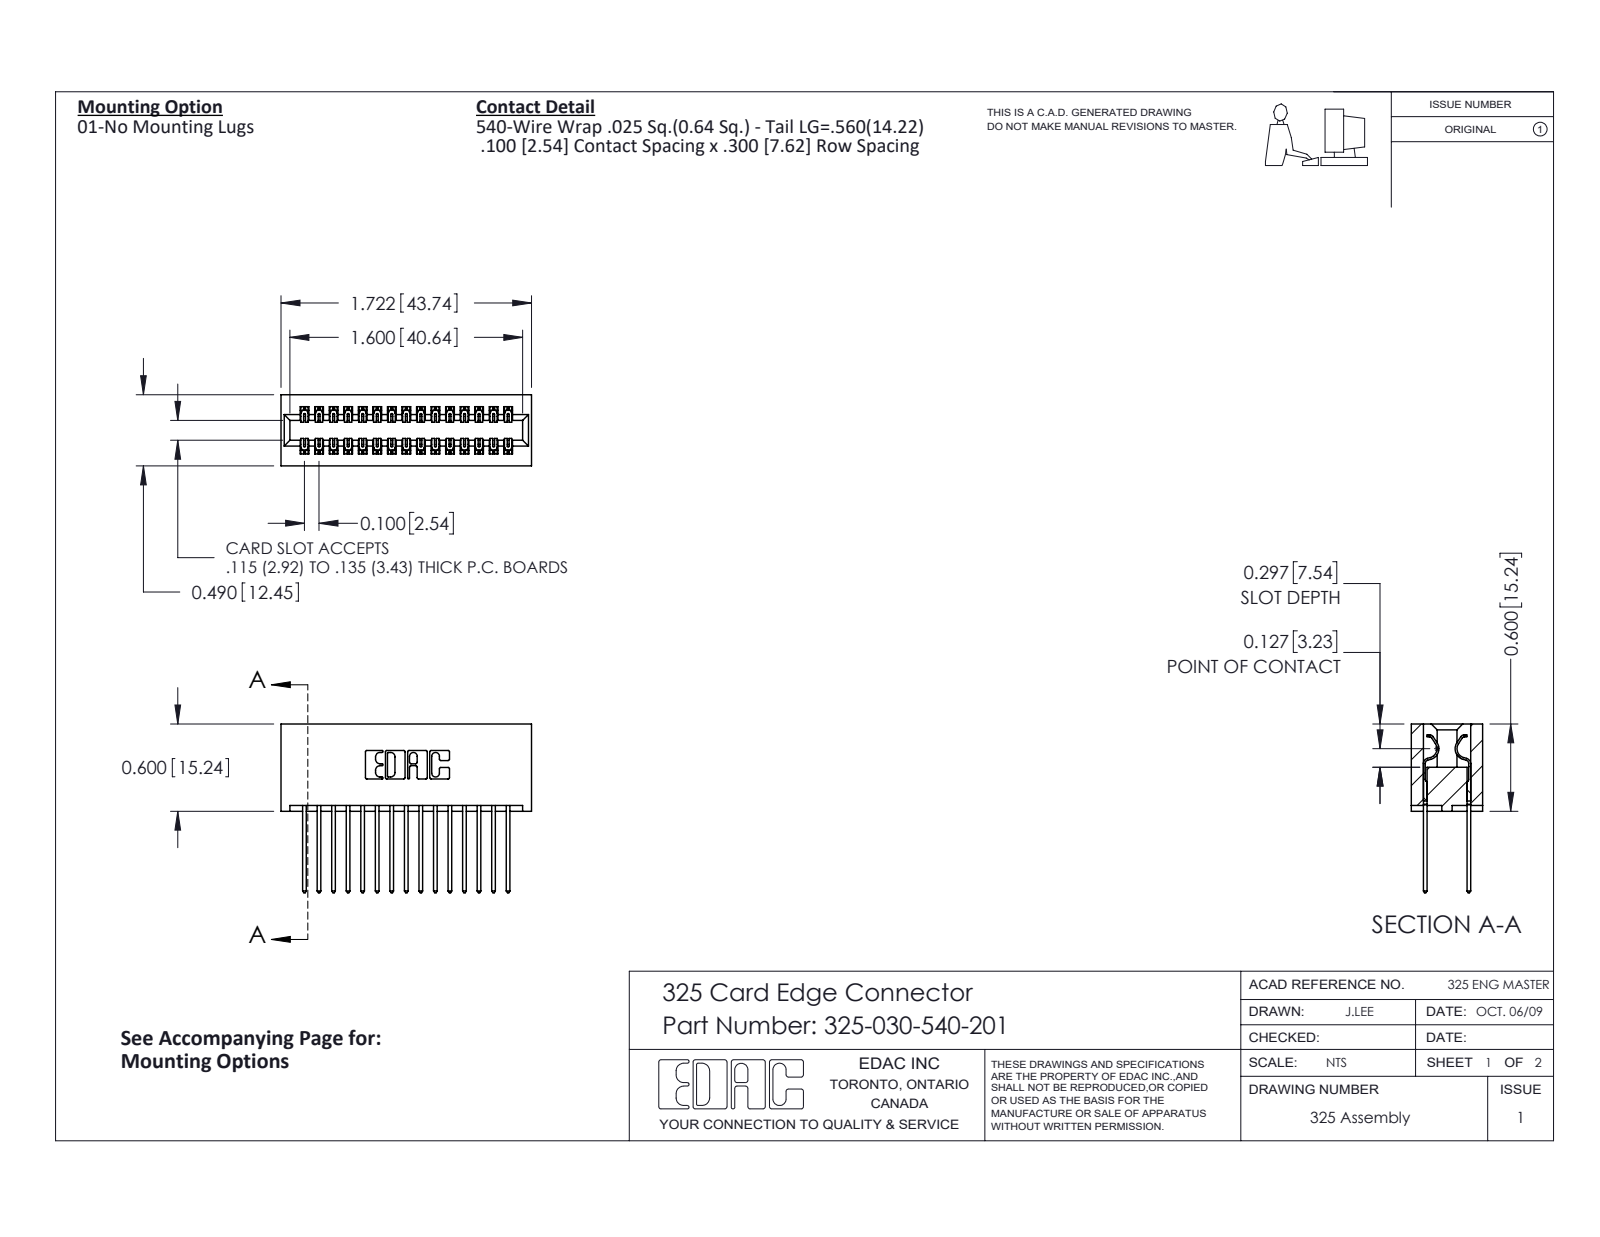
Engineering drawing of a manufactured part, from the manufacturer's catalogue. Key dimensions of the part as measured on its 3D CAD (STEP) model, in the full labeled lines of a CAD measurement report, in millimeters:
Part name (STEP PRODUCT): 325-030-540-201; 325-292-001_325-293-140; 325 Part_Lugless
STEP written by: SolidWorks 2016 (CONFIG_CONTROL_DESIGN)
Units: millimetres
Bodies: 31 solids, 1666 faces (1146 planar, 520 cylindrical, 0 other)
Overall size (bounding box): 43.7 × 29.5 × 12.4
Volume: 6 130 mm³ · Surface area: 7 974 mm²
Partial cylindrical surfaces — rounded edges, fillets, slot ends (radius × count): R0.2 ×45, R0.3 ×30, R0.3 ×22, R0.2 ×6, R0.8 ×6, R0.7 ×3, R0.4 ×2, R0.6 ×2
Main face-to-face distances: 2.1, 10.3, 7.6, 2.7, 9.7, 0.6, 8.3, 12.4, 2.5, 5.1
